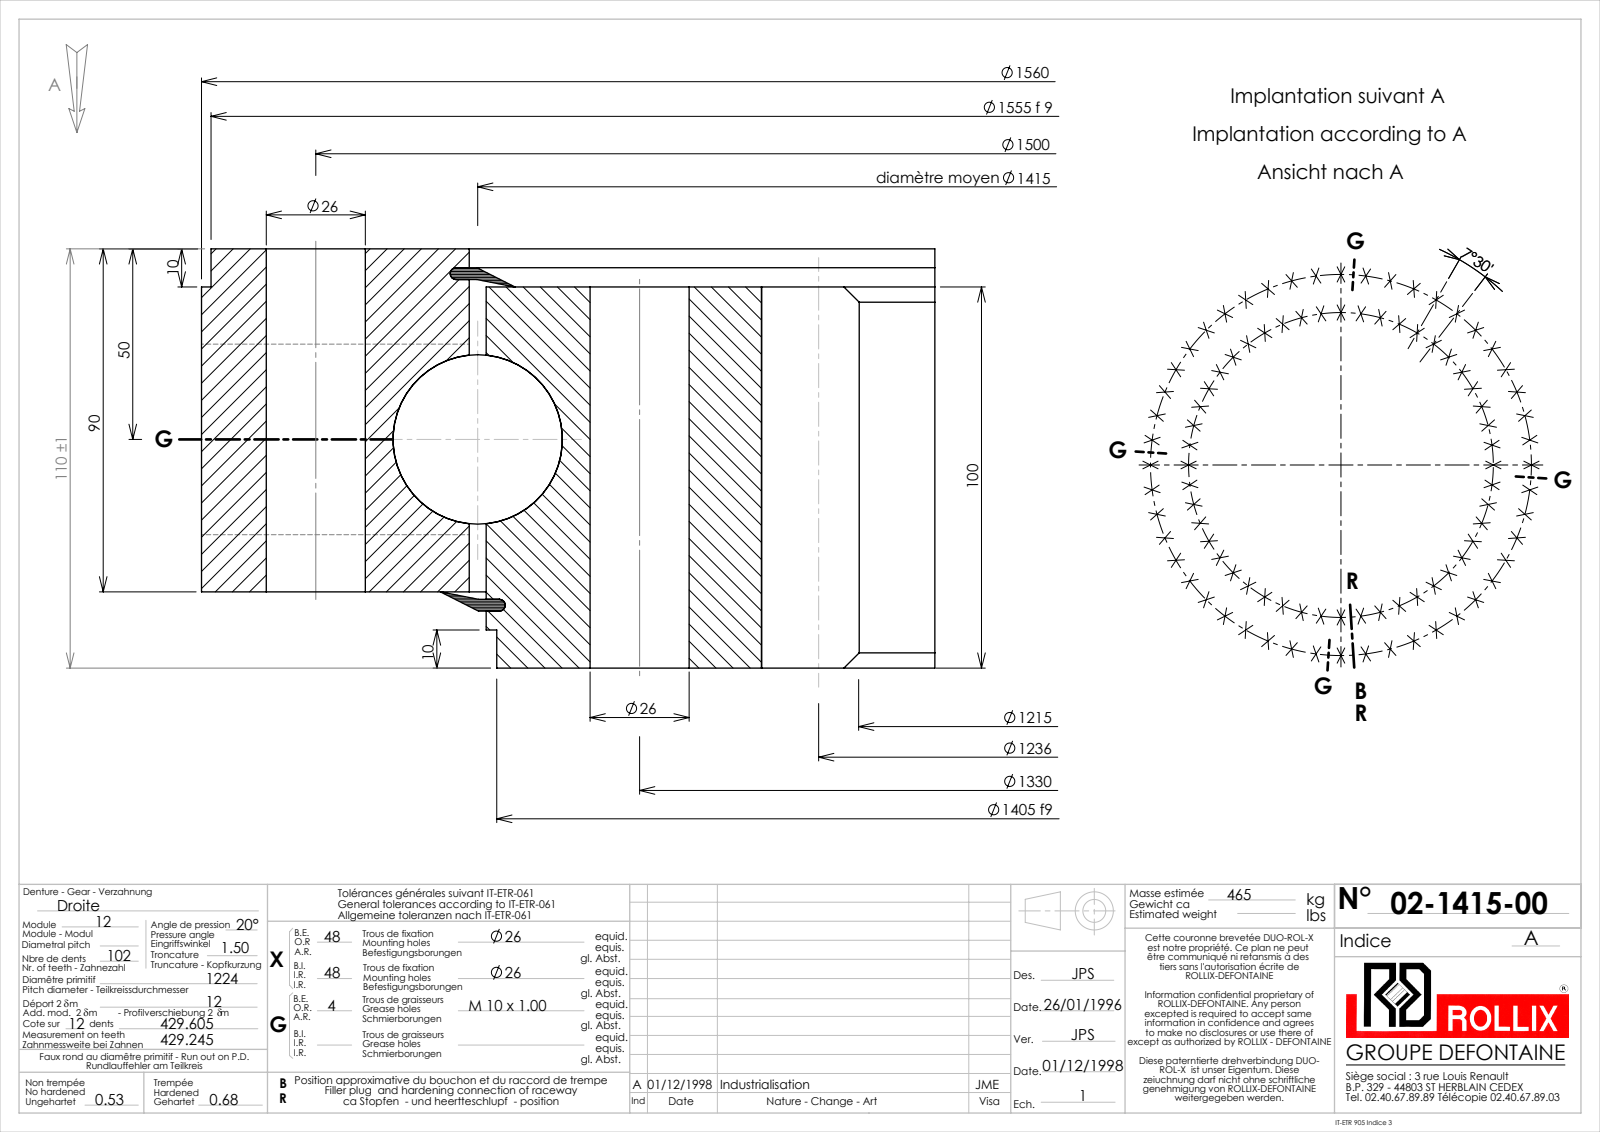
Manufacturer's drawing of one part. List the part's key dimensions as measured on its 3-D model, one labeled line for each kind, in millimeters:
Part name (STEP PRODUCT): 02-1415-00
STEP written by: SolidWorks 2016 (CONFIG_CONTROL_DESIGN)
Units: millimetres
Bodies: 5 solids, 873 faces (218 planar, 423 cylindrical, 232 other)
Overall size (bounding box): 1560 × 1560 × 110
Volume: 54 500 000 mm³ · Surface area: 4 649 000 mm²
Round holes (diameter × count): ⌀26 ×96, ⌀9 ×4, ⌀1419.44 ×1
Round bosses / shafts (diameter × count): ⌀1560 ×1, ⌀1555 ×1, ⌀1410.56 ×1, ⌀1405 ×1
Partial cylindrical surfaces — rounded edges, fillets, slot ends (radius × count): R607.5 ×1, R633 ×1
Main face-to-face distances: 100, 10, 90, 20, 80, 110, 5.05, 85.05, 3.1, 1.95
Hole centre spacings: 173.6, 344.23, 665, 86.99, 259.47, 427.52, 738.91, 508.97
